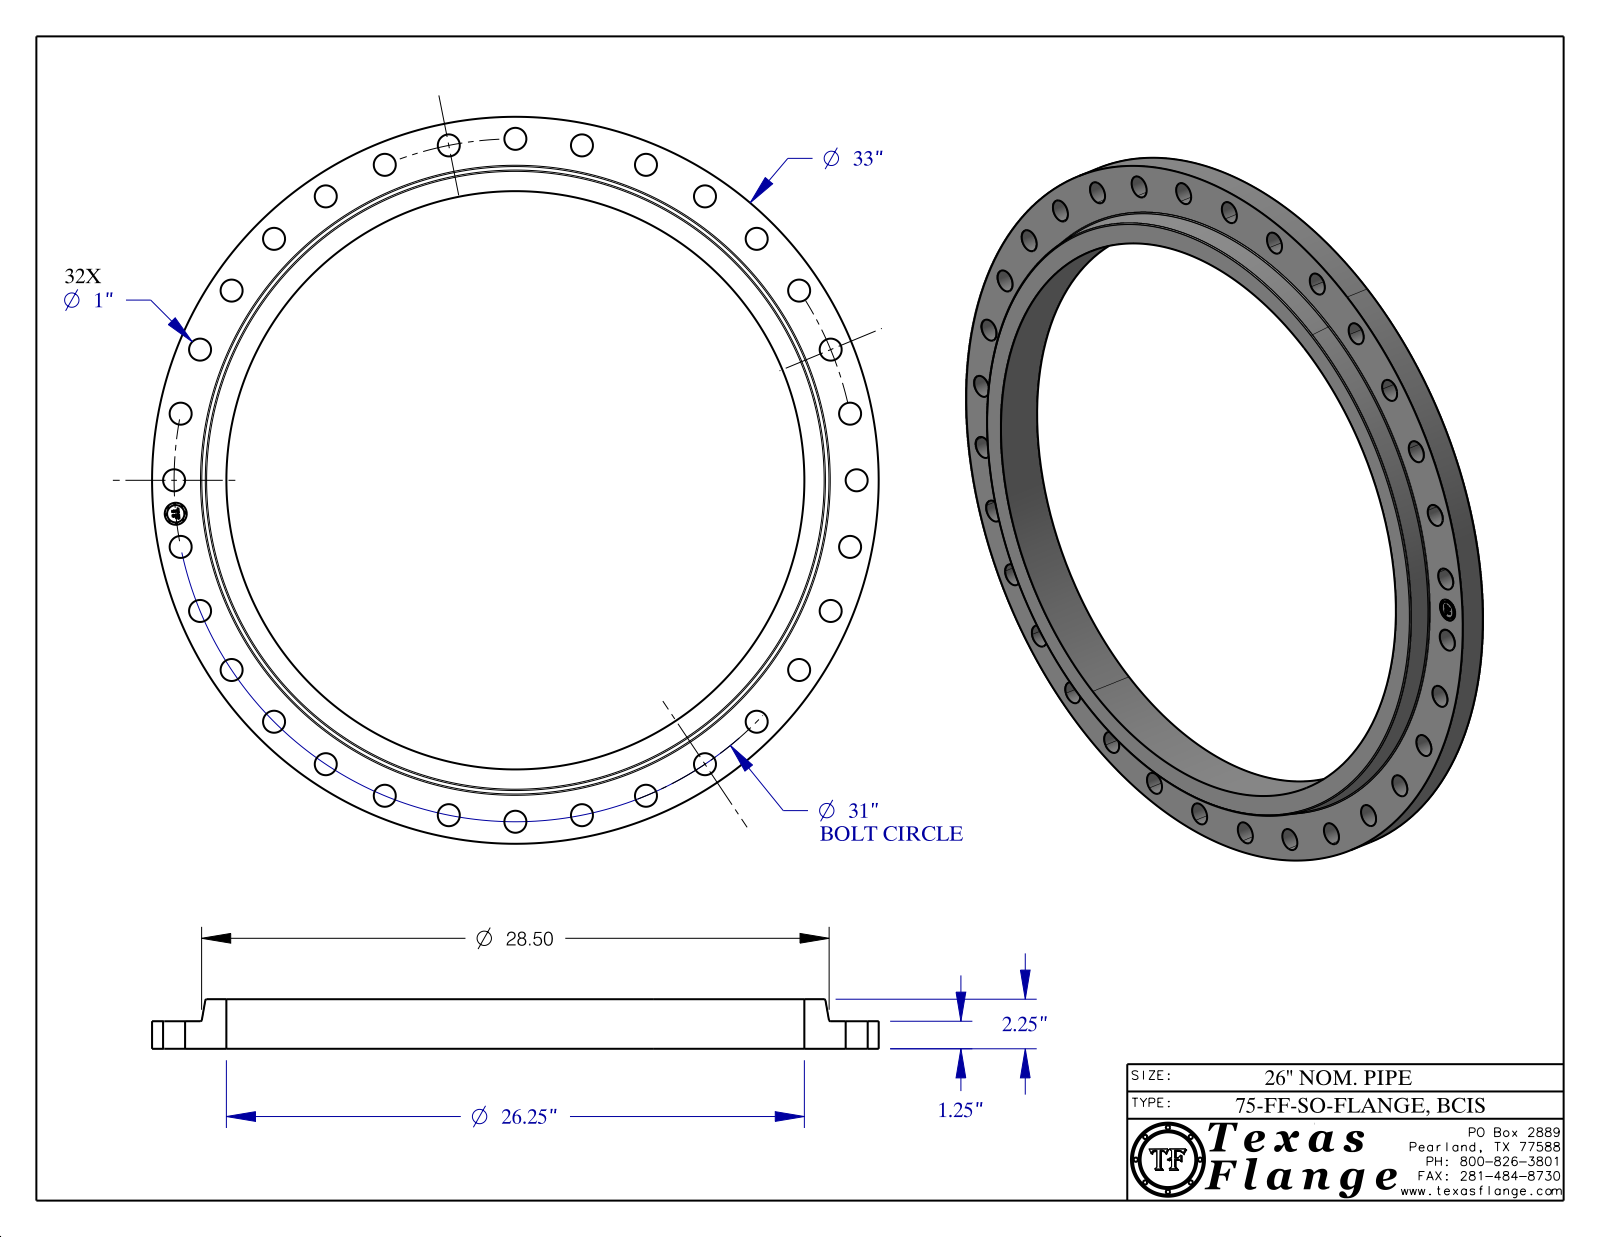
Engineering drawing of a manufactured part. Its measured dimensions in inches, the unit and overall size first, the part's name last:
Units: inches
Overall size (bounding box): 33 × 33 × 2.25
Round holes (diameter × count): ⌀1 ×33, ⌀26.25 ×1
Round bosses / shafts (diameter × count): ⌀0.061 ×8, ⌀33 ×1, ⌀0.788 ×1
Main face-to-face distances: 1.25, 2.25, 1, 0.015, 1.235, 1.015, 0.298, 0.292, 0.054, 0.193
Hole centre spacings: 30.851, 3.039, 8.999, 14.613, 23.963, 25.776, 15.5, 17.223
Volume: 450.1 in³ · Surface area: 1 091 in²
Bodies: 1 solid, 462 faces (368 planar, 88 cylindrical, 6 other)
Part name (STEP PRODUCT): BCIS, Class 75-FF-SO
STEP written by: CATIA V5 STEP AP214 (AUTOMOTIVE_DESIGN)
